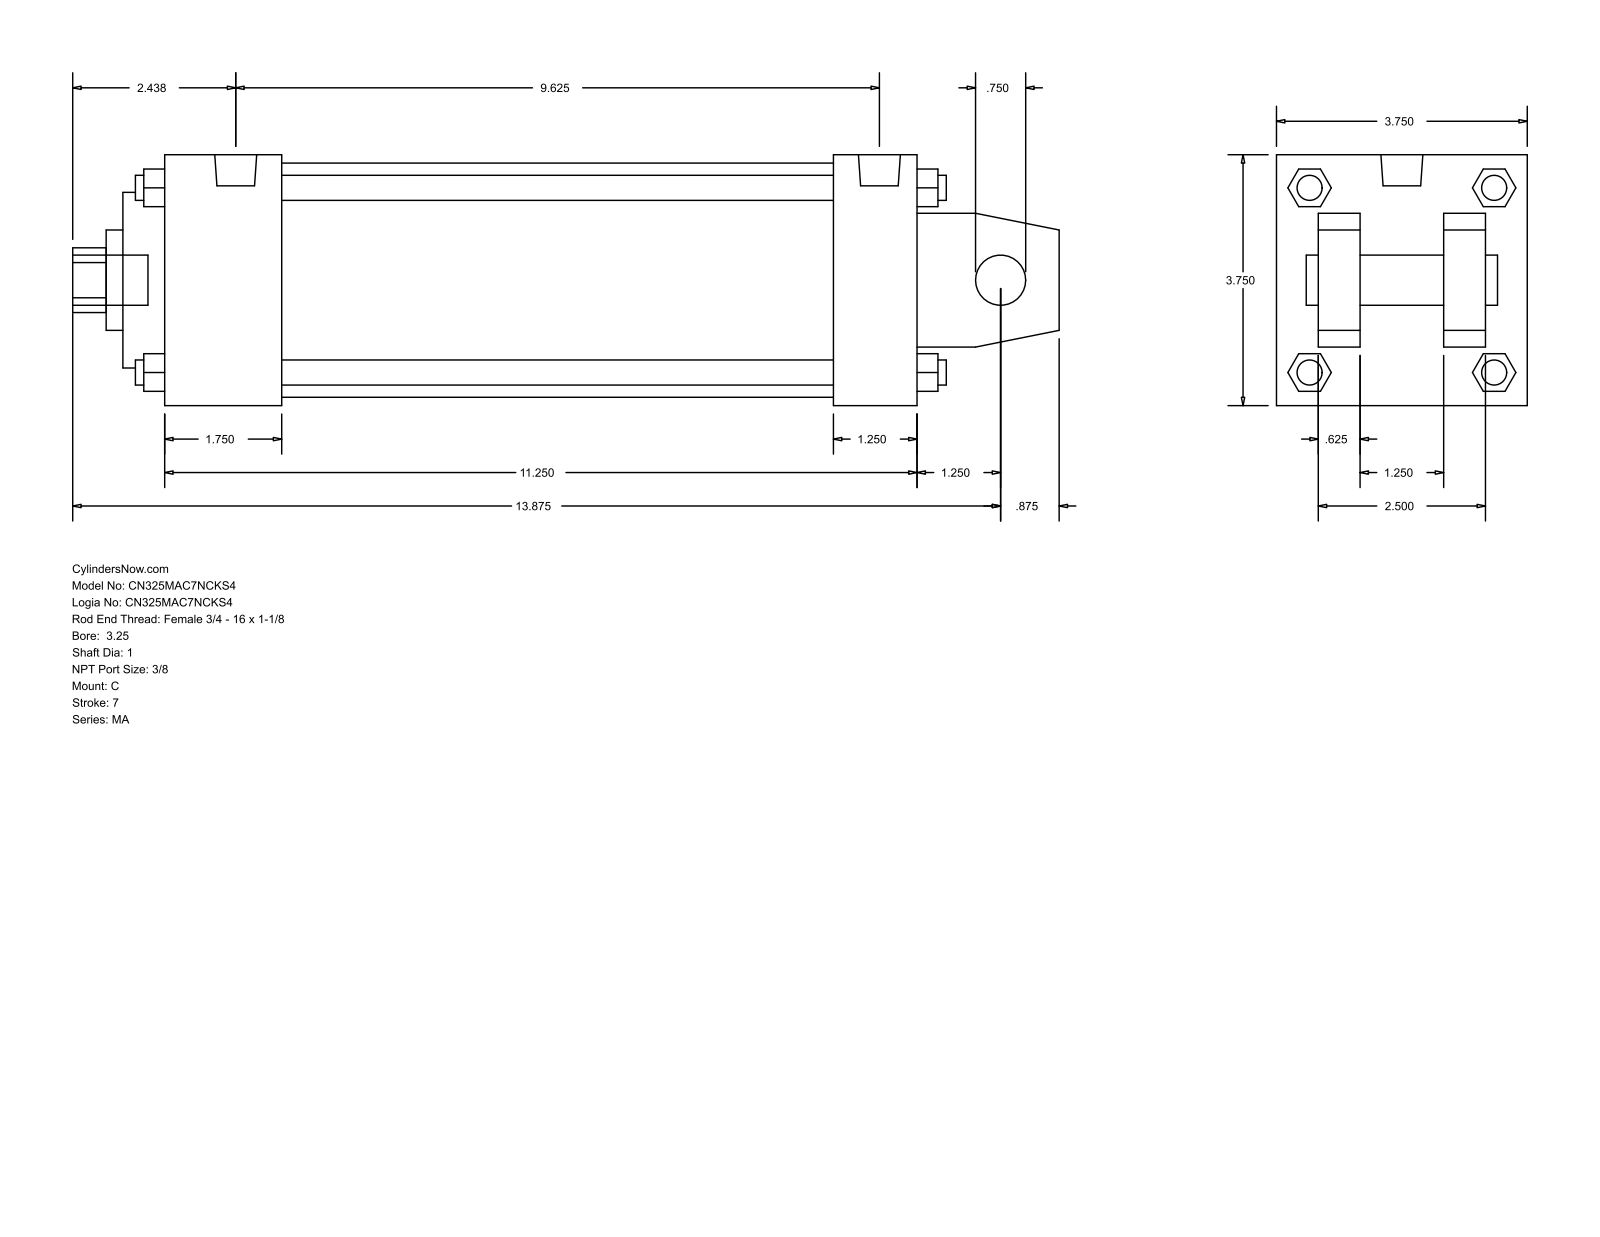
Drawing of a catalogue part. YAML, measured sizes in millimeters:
part_name: "MA_C__0325_1"
step_written_by: "GSSL Pune (CONFIG_CONTROL_DESIGN)"
units: millimeters
bodies: {solids: 0, faces: 141, planar: 109, cylindrical: 32, other: 0}
overall_size: [374.65, 95.25, 95.25]
round_holes:
  - {diameter: 19.05, count: 1}
  - {diameter: 25.4, count: 1}
  - {diameter: 38.1, count: 1}
  - {diameter: 66.67, count: 1}
  - {diameter: 88.9, count: 1}
round_bosses_or_shafts:
  - {diameter: 11.11, count: 4}
  - {diameter: 9.53, count: 4}
  - {diameter: 15.93, count: 2}
  - {diameter: 19.05, count: 1}
partial_cylinders:
  - {radius: 12.29, count: 1}
face_to_face_distances: [95.24, 15.87, 63.5, 285.76, 31.74, 79.37, 47.63, 254.01, 31.75, 44.46]
